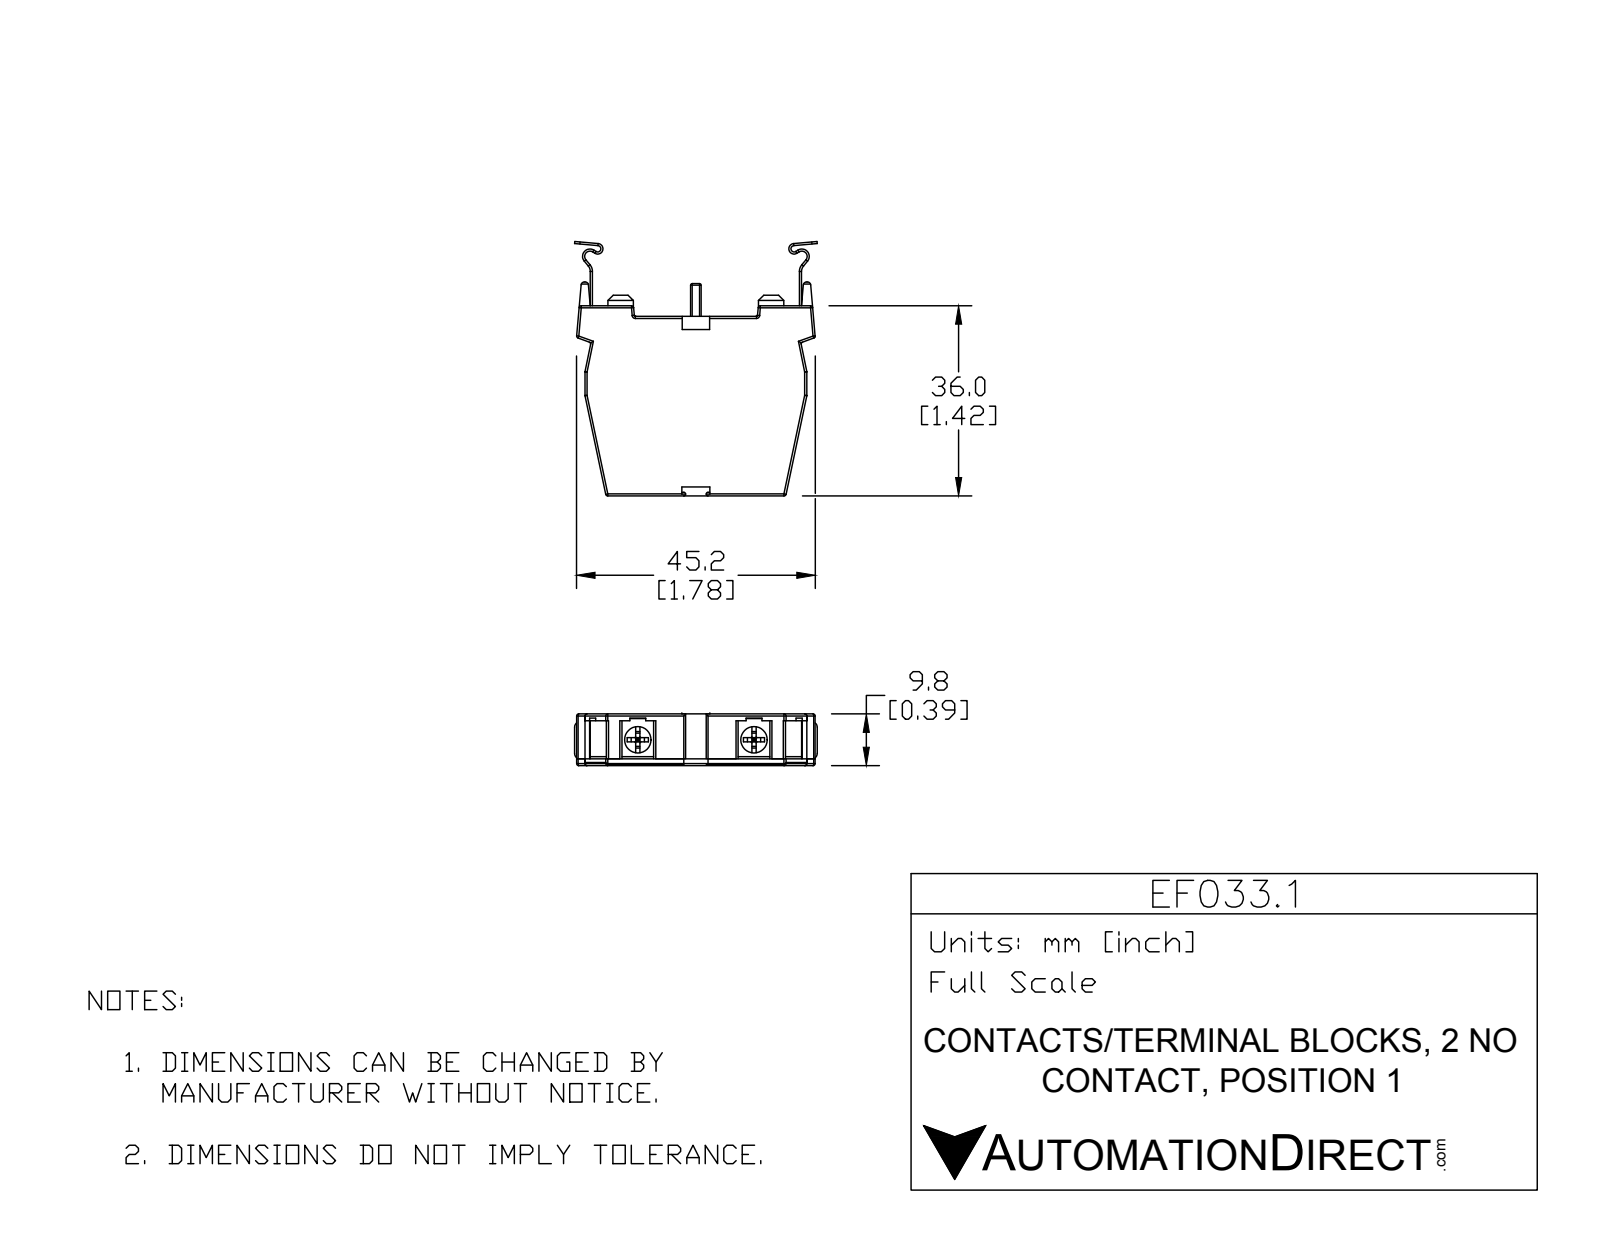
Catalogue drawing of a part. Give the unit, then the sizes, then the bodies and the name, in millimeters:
Units: millimetres
Overall size (bounding box): 48.16 × 46.28 × 9.8
Round holes (diameter × count): ⌀5 ×4
Round bosses / shafts (diameter × count): ⌀4 ×4, ⌀4.75 ×2
Partial cylindrical surfaces — rounded edges, fillets, slot ends (radius × count): R0.25 ×44, R0.5 ×8, R1 ×6, R0.6 ×4, R0.6 ×2, R1 ×2, R1.4 ×2, R1.6 ×2
Main face-to-face distances: 9.8, 1.4, 8.4, 34, 7, 2, 0.4, 3.18, 37.18, 36
Hole centre spacings: 21.81
Volume: 12 135 mm³ · Surface area: 6 604 mm²
Bodies: 7 solids, 299 faces (173 planar, 104 cylindrical, 22 other)
Part name (STEP PRODUCT): EF033.1
STEP written by: SolidWorks 2015 (AUTOMOTIVE_DESIGN)
